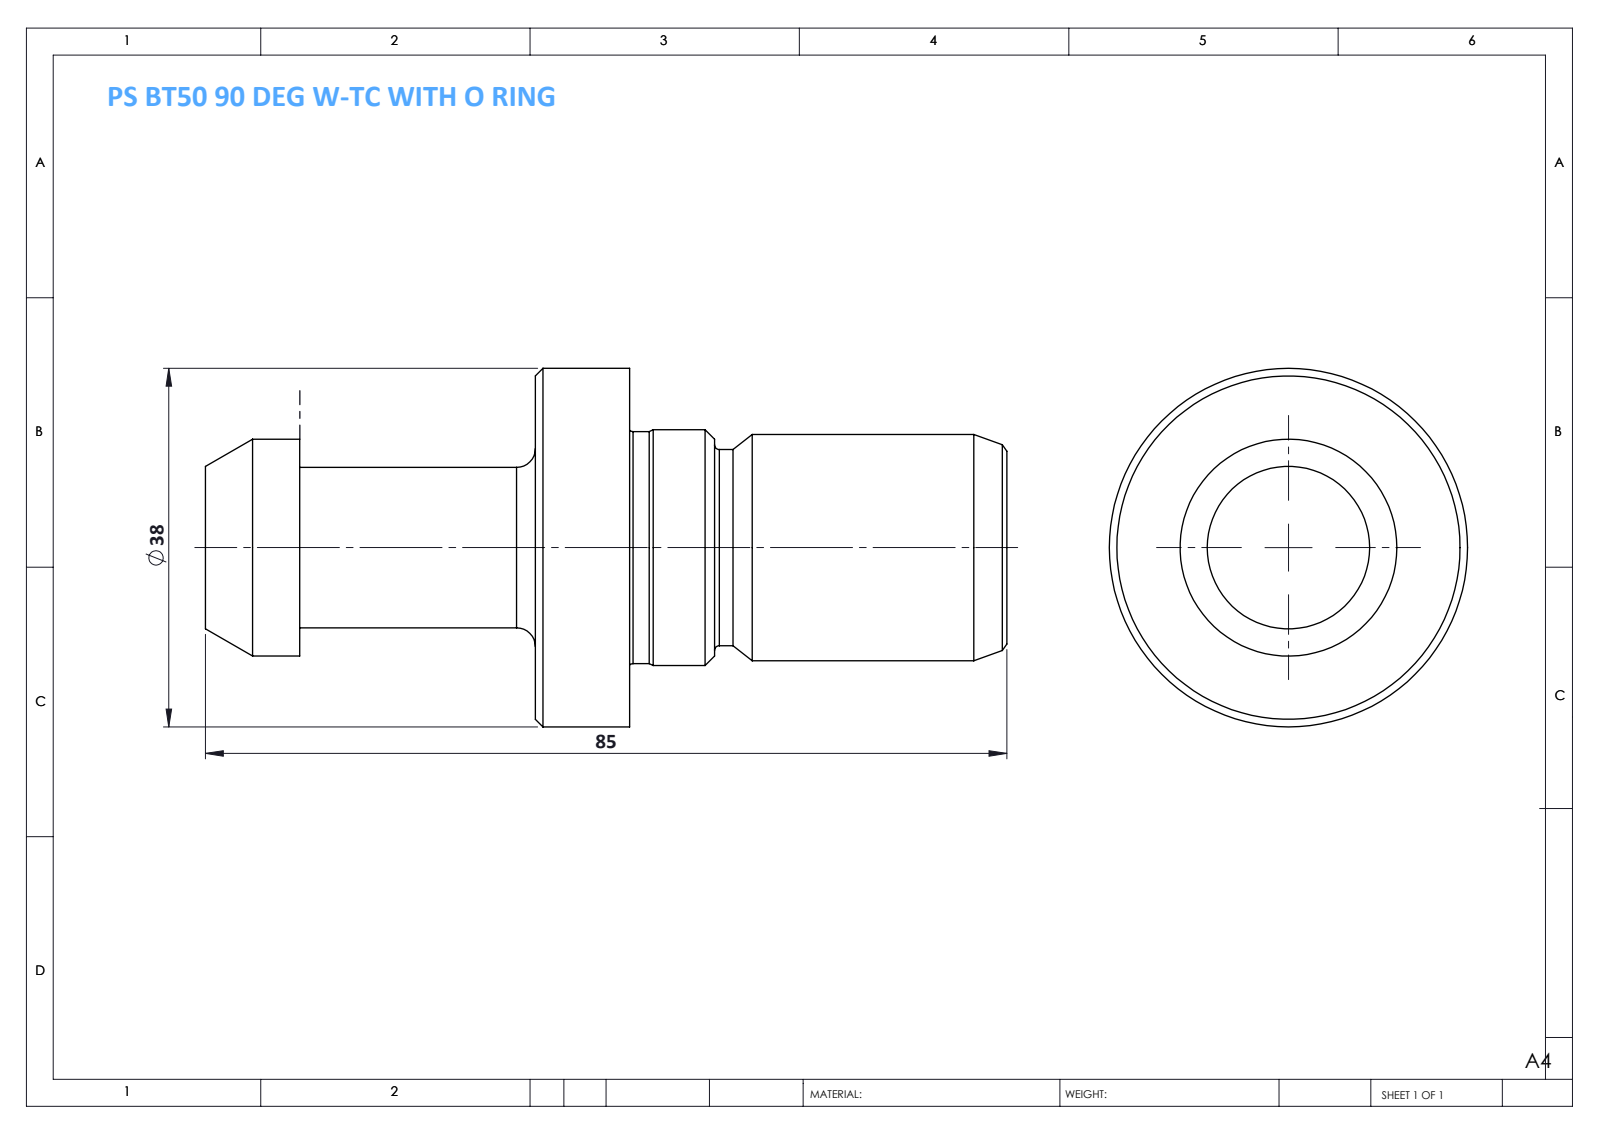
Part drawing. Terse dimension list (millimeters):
name: PS BT50 90 DEG W-TC WITH O RING
written by: SolidWorks 2014 (CONFIG_CONTROL_DESIGN)
unit: mm
bodies: 1 solid, 42 faces (6 planar, 14 cylindrical, 22 other)
size: 85 × 38 × 38
volume: 38 561 mm³; area: 8 633 mm²
bosses: 1× ⌀38, 1× ⌀25, 1× ⌀24.6, 1× ⌀24, 1× ⌀23, 1× ⌀20.8, 1× ⌀17
face distances: 10, 35, 40, 50, 85, 45, 75, 25, 31, 9
